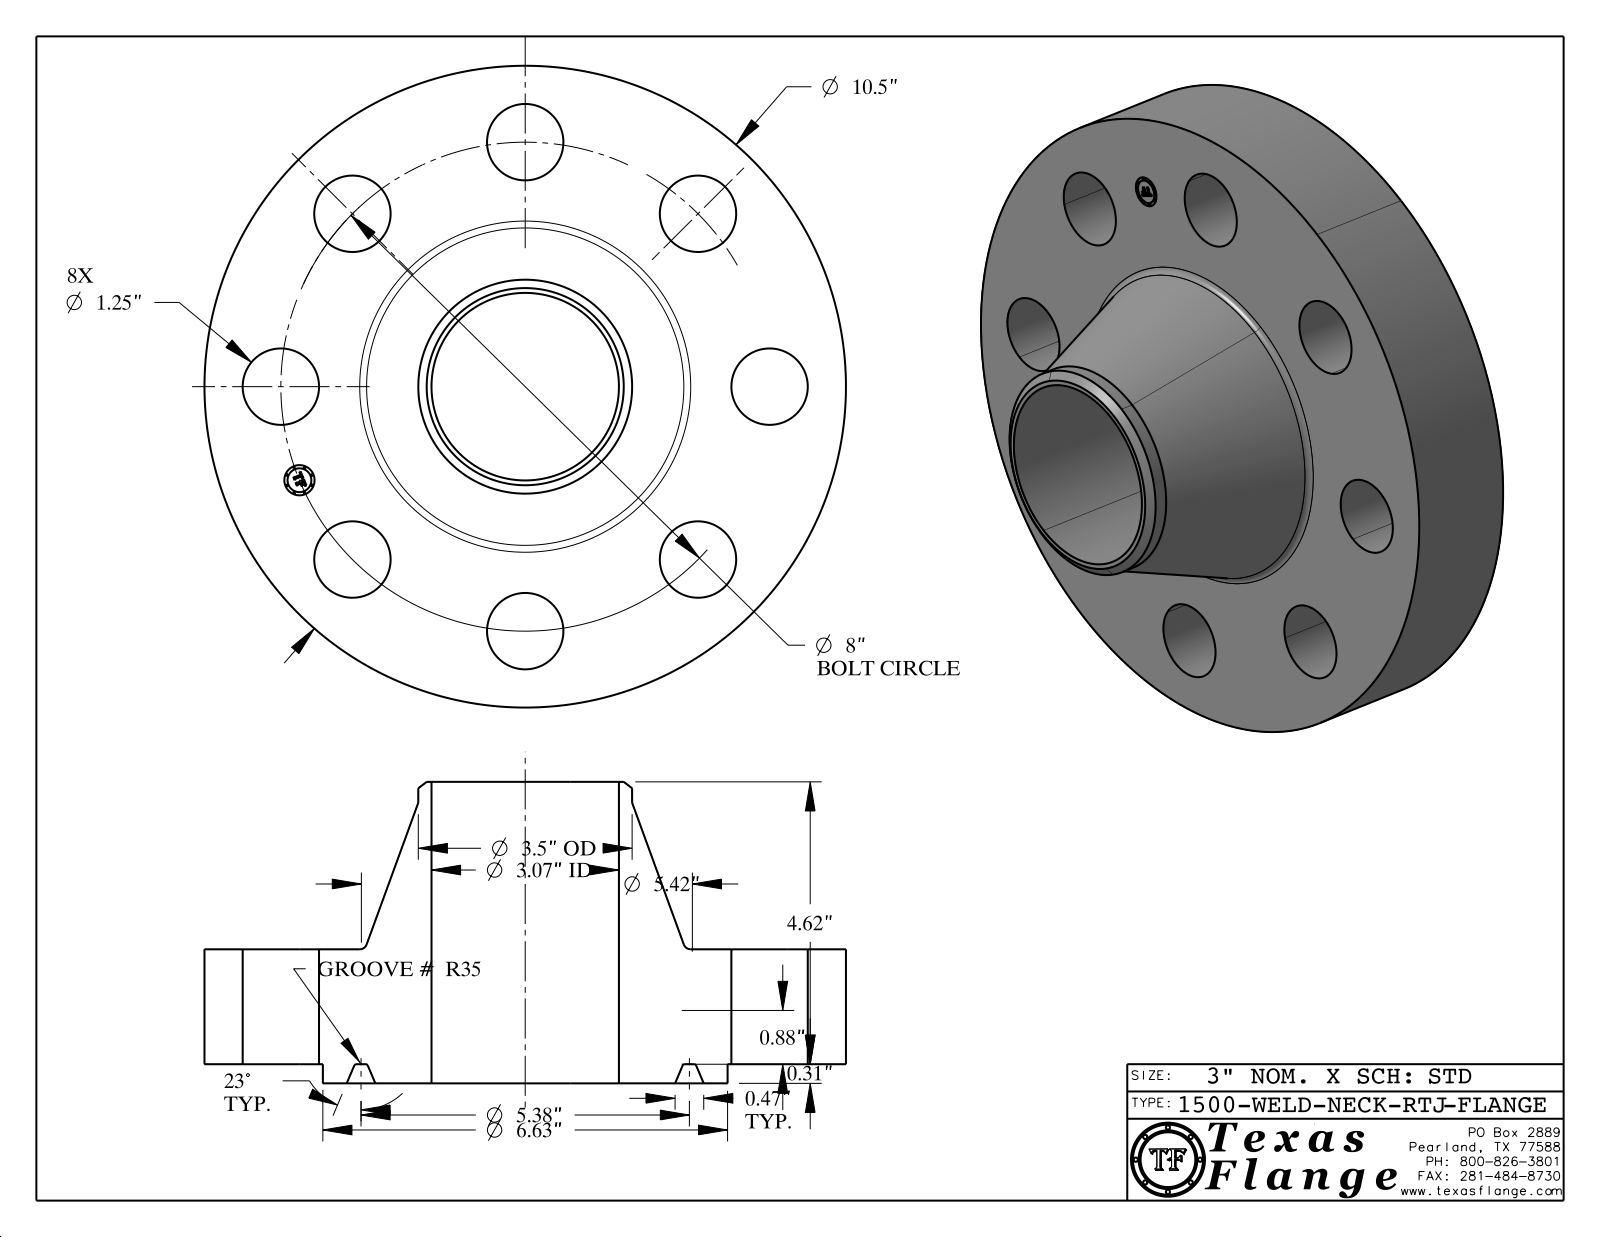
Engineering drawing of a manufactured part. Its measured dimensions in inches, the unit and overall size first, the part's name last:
Units: inches
Overall size (bounding box): 10.5 × 10.5 × 4.933
Round holes (diameter × count): ⌀1.25 ×8, ⌀0.495 ×1, ⌀3.068 ×1
Round bosses / shafts (diameter × count): ⌀0.03 ×8, ⌀10.5 ×1, ⌀6.625 ×1, ⌀3.5 ×1, ⌀0.39 ×1
Main face-to-face distances: 1.88, 0.313, 2.193, 4.933, 4.62, 2.74, 0.015, 2.178, 1.865, 2.755
Hole centre spacings: 4, 3.061, 5.657, 7.391, 1.561, 6.652, 7.846, 8
Volume: 156.6 in³ · Surface area: 346.5 in²
Bodies: 1 solid, 429 faces (371 planar, 44 cylindrical, 14 other)
Part name (STEP PRODUCT): 1500-WELD-NECK-RTJ
STEP written by: CATIA V5 STEP AP214 (AUTOMOTIVE_DESIGN)
